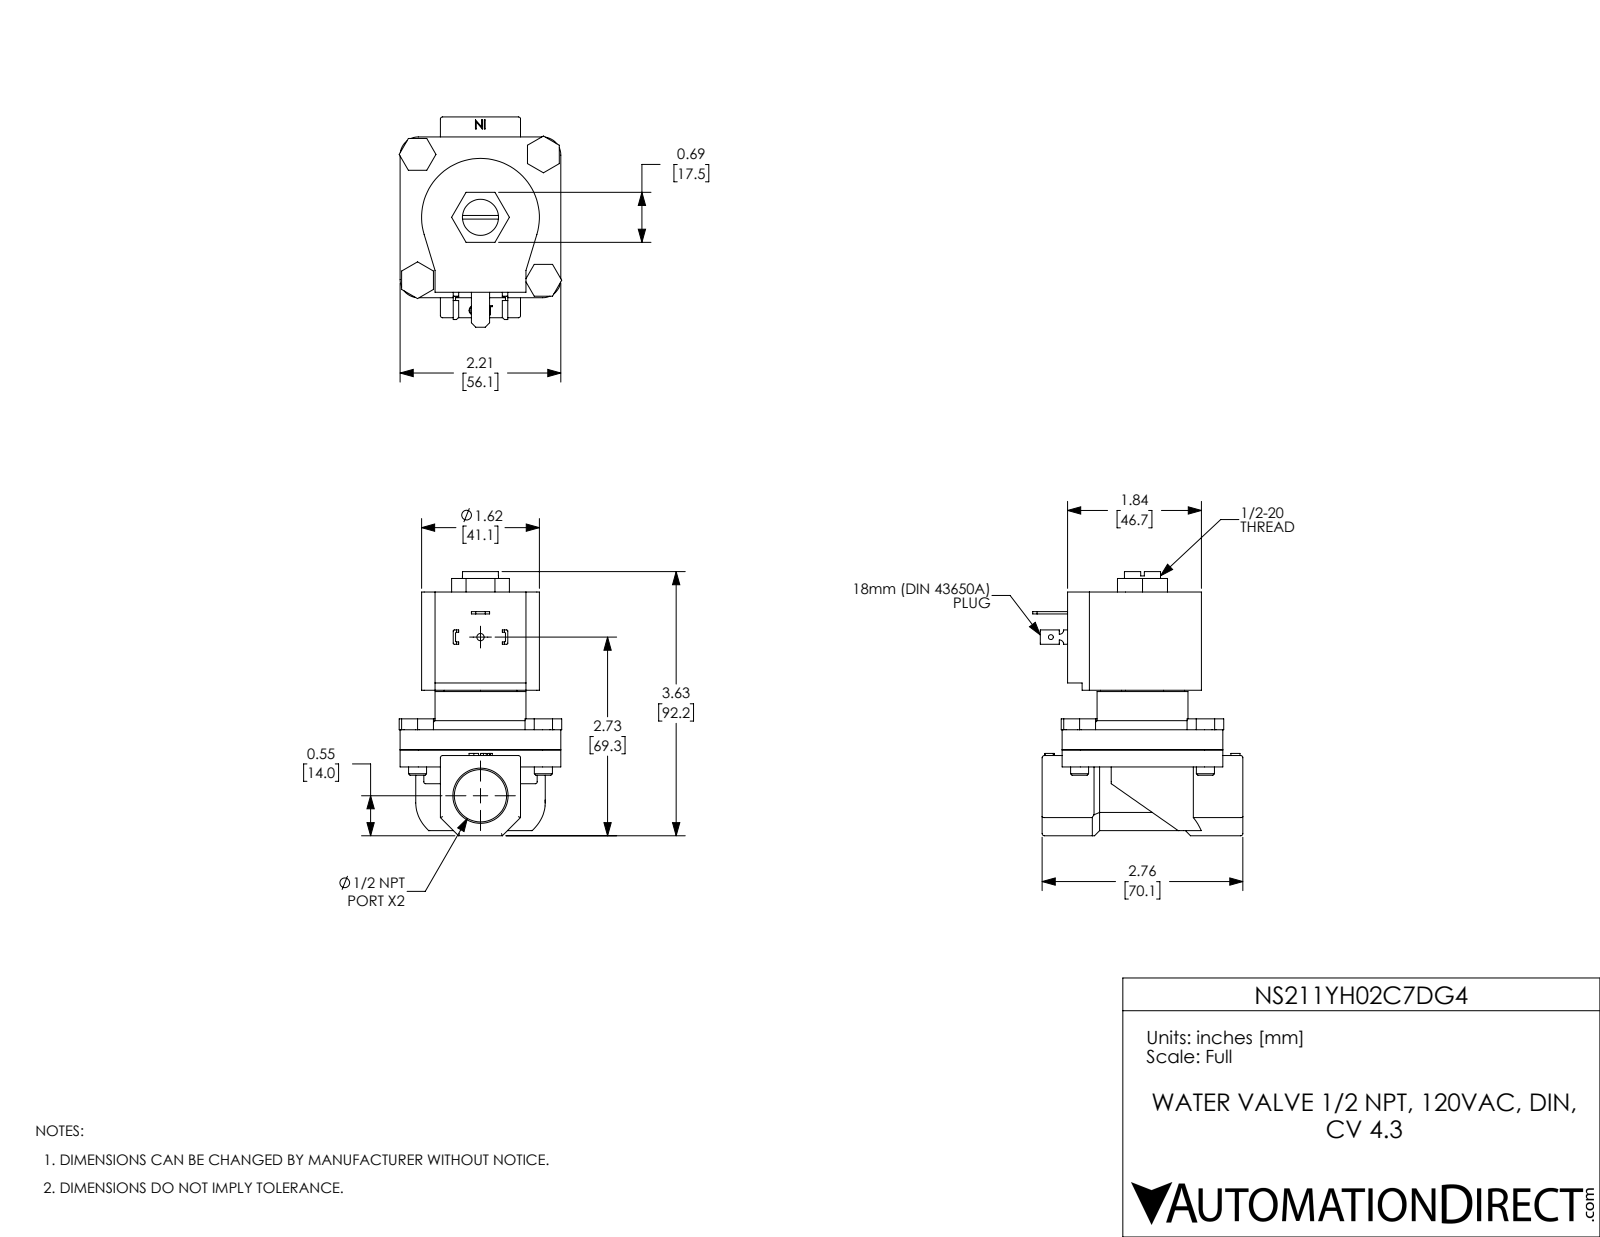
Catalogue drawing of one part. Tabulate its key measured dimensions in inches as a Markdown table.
| quantity | value |
| --- | --- |
| part name | NS211YH24C7DG4 |
| STEP written by | SolidWorks 2024 (CONFIG_CONTROL_DESIGN) |
| units | inches |
| bodies | 11 solids, 330 faces (196 planar, 99 cylindrical, 35 other) |
| overall size | 3.63 × 2.89 × 2.235 |
| volume | 9.198 in³ |
| surface area | 60.98 in² |
| round holes (diameter × count) | 0.25 × 4, 0.067 × 1, 0.1 × 1, 0.496 × 1, 0.512 × 1, 0.719 × 1, 1.155 × 1 |
| round bosses / shafts (diameter × count) | 0.248 × 4, 1.25 × 1 |
| partial cylindrical surfaces (radius × count) | 0.03 × 15, 0.015 × 8, 0.25 × 4, 0.06 × 2, 0.81 × 1, 0.89 × 1 |
| main face-to-face distances | 0.276, 2.169, 1.893, 0.554, 1.656, 0.236, 0.512, 2.405, 2.21, 1.102 |
| hole center spacings | 1.223, 1.73, 2.446, 2.18 |
